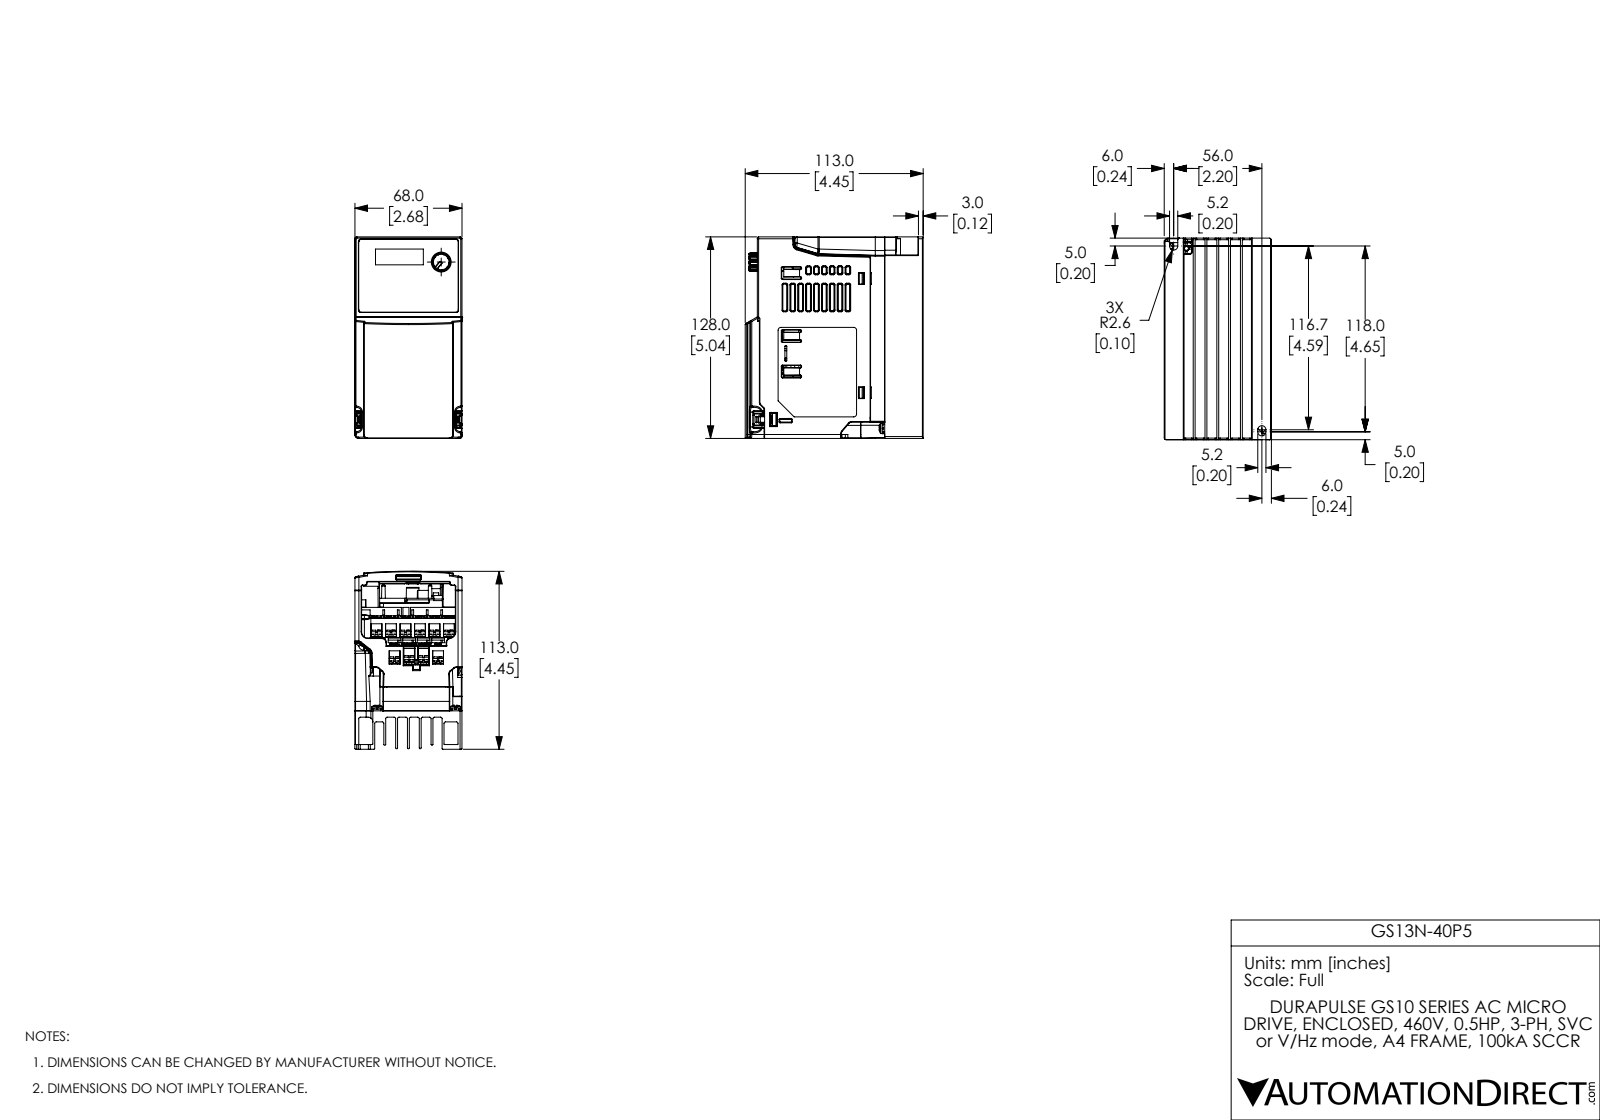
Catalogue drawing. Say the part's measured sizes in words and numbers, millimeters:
The part is named "GS13N-40P5". Its 3-D file was written by "SolidWorks 2017 (AUTOMOTIVE_DESIGN)". It is 33 solids with 5891 faces: 3116 planar, 1269 cylindrical and 1506 other. Overall it measures 128 by 113 by 68.05 millimeters. Its volume is 159 808 cubic millimeters and its surface area 166 783 square millimeters. Round holes: 10 of diameter 3.15, 2 of diameter 4.8, 1 of diameter 3.9, 1 of diameter 10.9, 1 of diameter 12.6. Round bosses or shafts: 12 of diameter 6.8, 12 of diameter 2.76, 10 of diameter 3.5, 2 of diameter 4.2, 2 of diameter 3.4. Partial cylindrical surfaces (rounded edges, fillets, slot ends): 152 of radius 0.5, 144 of radius 0.3, 85 of radius 0.4, 70 of radius 0.2, 32 of radius 1, 30 of radius 0.8, 25 of radius 3, 23 of radius 1.2. The main face-to-face distances are 7.5, 1.2, 15, 68, 6, 29.5, 6.3, 8.7, 22, 14.5. The hole center spacings are 9.2, 18.4, 14.34, 15.74, 18.23, 27.6, 21.43, 25.07.
